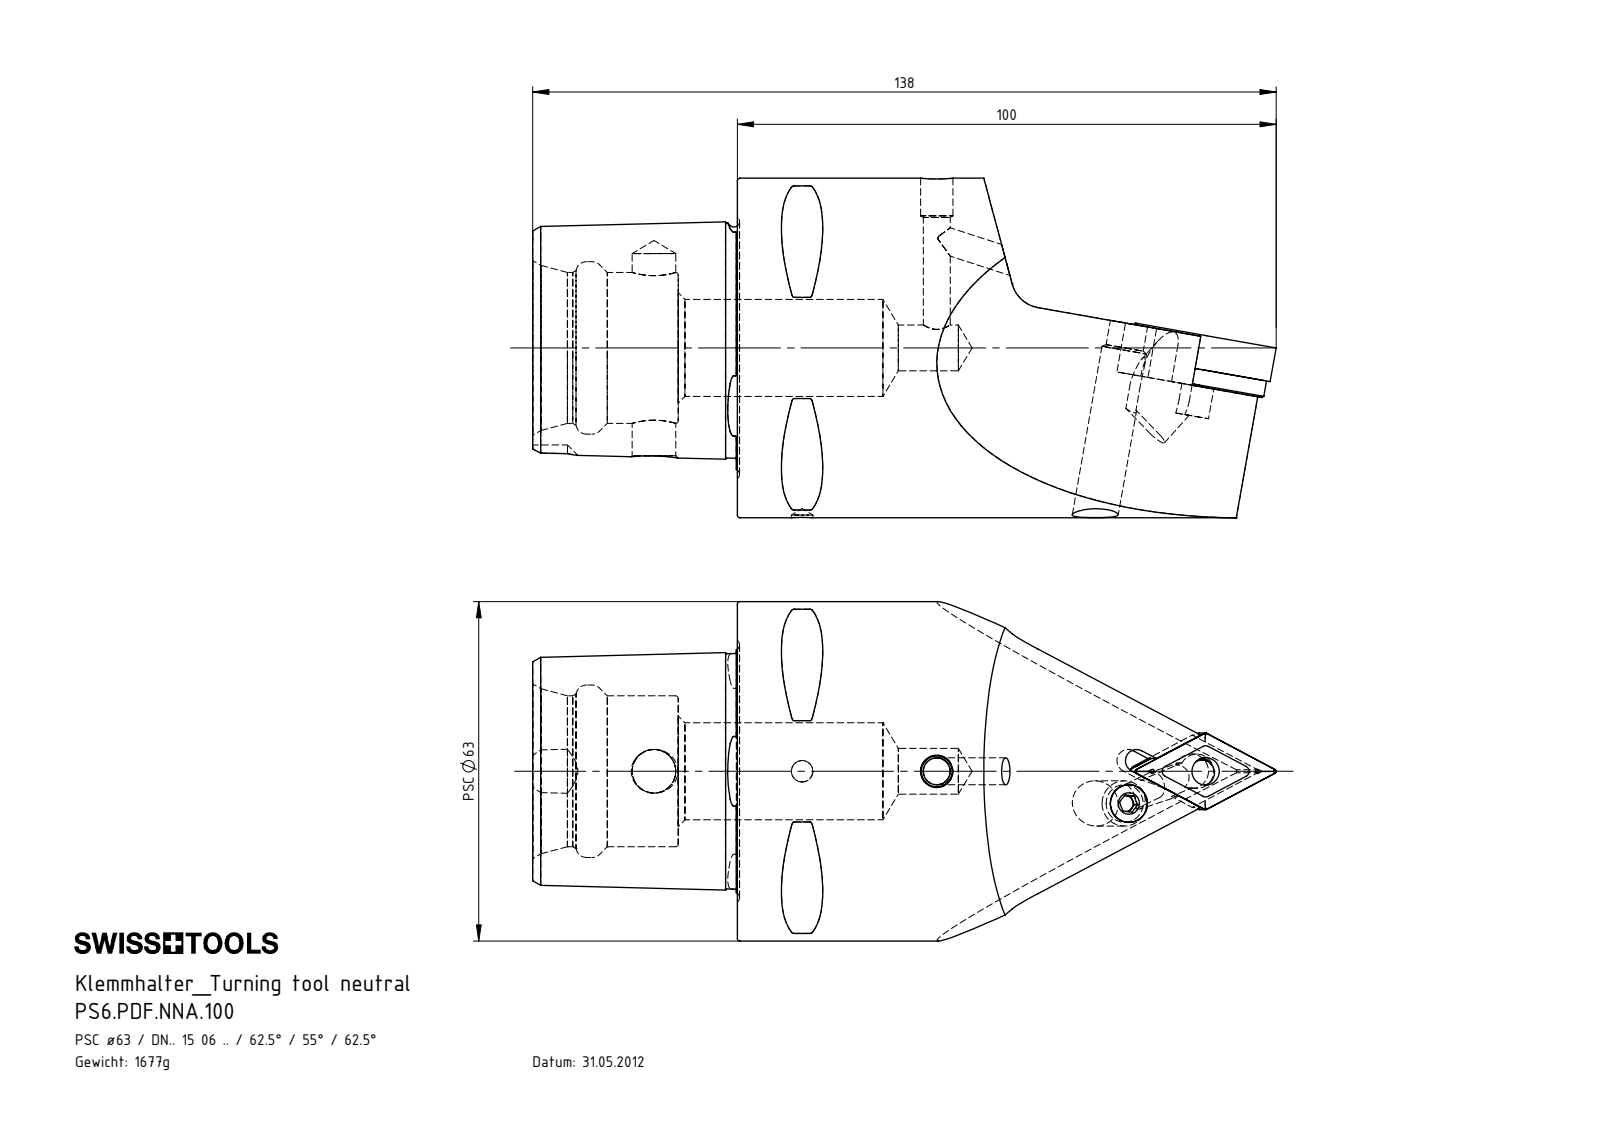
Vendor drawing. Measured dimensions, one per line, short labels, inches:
name: WCD-ER4.101.017_A; PS6.PDF.NNA.100; WDF-ER2.101.003_A; WCD-ER1.101.000 (+4 more)
written by: SolidWorks 2017 (AUTOMOTIVE_DESIGN)
unit: in
bodies: 8 solids, 248 faces (89 planar, 51 cylindrical, 108 other)
size: 5.433 × 2.48 × 2.48
volume: 13.21 in³; area: 53.68 in²
holes: 2× ⌀0.197, 1× ⌀0.157, 1× ⌀0.203, 1× ⌀0.252, 1× ⌀0.276, 1× ⌀0.319, 1× ⌀0.331, 1× ⌀0.335, 1× ⌀0.709, 1× ⌀1.102, 1× ⌀1.26
bosses: 1× ⌀2.48, 1× ⌀0.315, 1× ⌀0.311, 1× ⌀0.252, 1× ⌀0.236, 1× ⌀0.185, 1× ⌀0.14
rounds: 8× R0.02, 4× R0.016, 4× R0.039, 2× R0.098, 2× R0.126, 2× R0.236, 1× R0.083, 1× R0.093
face distances: 0.488, 1.496, 0.238, 0.98, 0.125, 0.363, 0.5, 1.063, 0.433, 2.197
hole spacings: 0.615, 0.984, 1.083, 2.067
